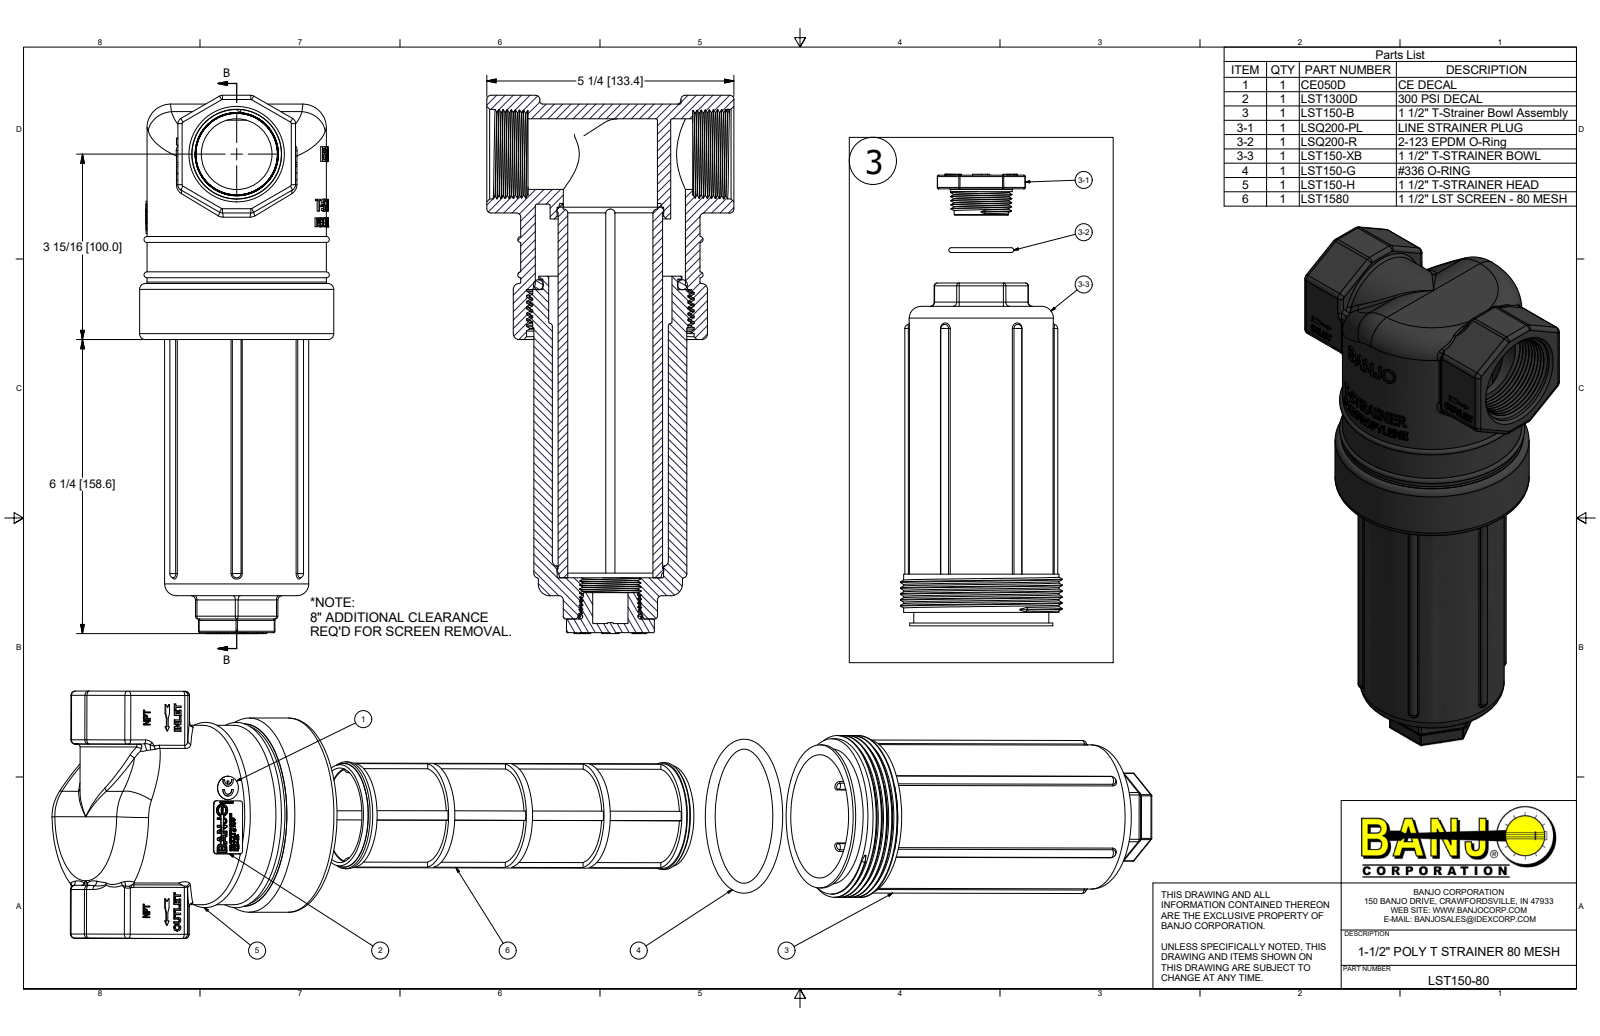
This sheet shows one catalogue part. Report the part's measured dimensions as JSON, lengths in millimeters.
{"part_name": "LST150-80; CE050D; LST1300D; LST150-B (+6 more)", "step_written_by": "Autodesk Inventor 2018 (AUTOMOTIVE_DESIGN)", "units": "millimeters", "bodies": {"solids": 8, "faces": 3126, "planar": 1685, "cylindrical": 290, "other": 1151}, "overall_size": [290.4, 133.4, 104.8], "volume_mm3": 812000, "surface_area_mm2": 311000, "round_holes": [[4.6, 1], [6.5, 1], [19.1, 1], [38.1, 1], [46, 1], [50, 1], [50.8, 1], [57.4, 1], [57.5, 1], [66.5, 1], [81, 1], [87, 1]], "round_bosses_or_shafts": [[104.8, 1], [96.8, 1], [87.2, 1], [83.8, 1], [77.8, 1], [77.2, 1], [72.9, 1], [65.1, 1]], "partial_cylinders_radius": [[0.8, 44], [2.3, 34], [1.5, 16], [3.2, 10], [2, 6], [2.4, 6], [2.5, 4], [0.7, 2]], "face_to_face_distances": [63.5, 155.4, 255.5, 100.1, 23.4, 31.5, 247.6, 92.2, 8, 47]}
